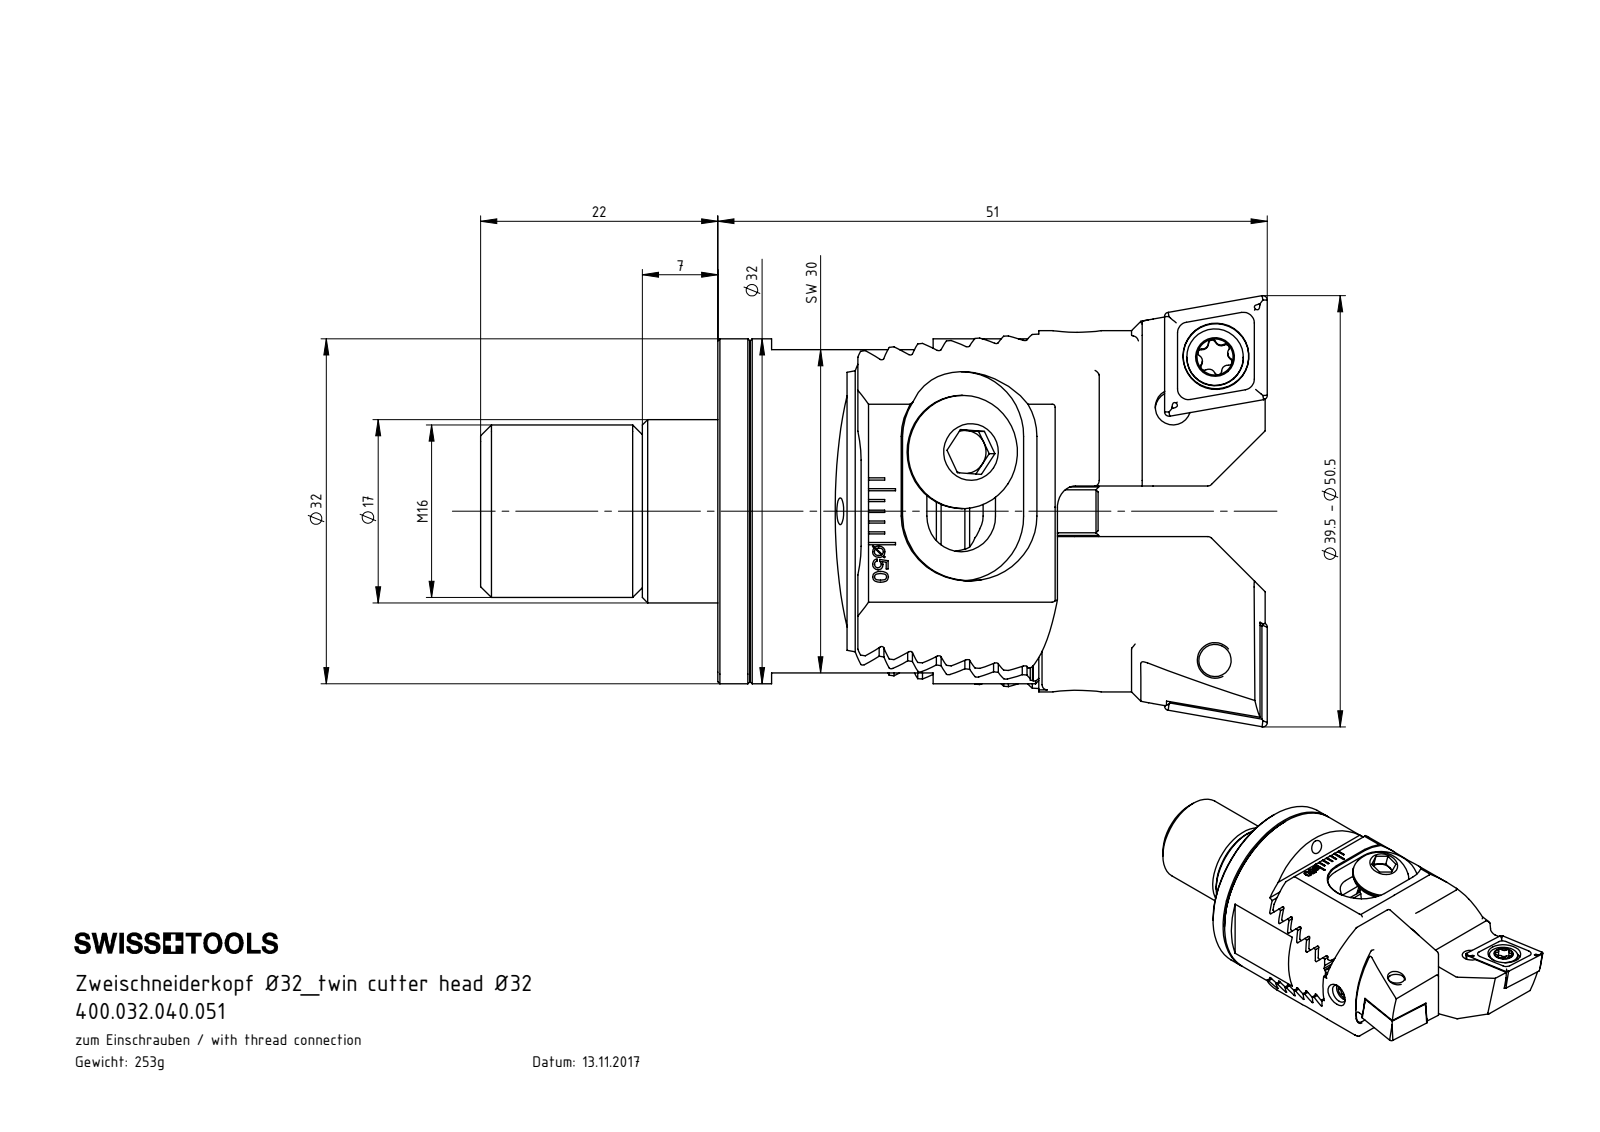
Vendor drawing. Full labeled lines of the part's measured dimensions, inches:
Part name (STEP PRODUCT): D32-D32.HP5.003_A; Z32-WCB.001.021; 400.032.040.051; HP5-ER2.012.030_A (+8 more)
STEP written by: SolidWorks 2017 (CONFIG_CONTROL_DESIGN)
Units: inches
Bodies: 16 solids, 985 faces (457 planar, 232 cylindrical, 296 other)
Overall size (bounding box): 2.874 × 1.575 × 1.26
Volume: 1.965 in³ · Surface area: 30.38 in²
Round holes (diameter × count): ⌀0.098 ×5, ⌀0.13 ×5, ⌀0.063 ×2, ⌀0.079 ×2, ⌀0.173 ×2, ⌀0.197 ×2, ⌀0.24 ×2, ⌀0.252 ×2, ⌀0.268 ×2, ⌀0.138 ×1, ⌀0.402 ×1, ⌀0.492 ×1
Round bosses / shafts (diameter × count): ⌀0.157 ×4, ⌀0.413 ×2, ⌀0.402 ×2, ⌀0.236 ×2, ⌀0.207 ×2, ⌀1.26 ×1, ⌀0.63 ×1, ⌀0.472 ×1
Partial cylindrical surfaces — rounded edges, fillets, slot ends (radius × count): R0.02 ×16, R0.008 ×14, R0.008 ×12, R0.013 ×12, R0.023 ×12, R0.079 ×4, R0.13 ×4, R0.236 ×4
Main face-to-face distances: 0.094, 0.187, 0.281, 0.118, 0.375, 0.375, 0.193, 0.469, 0.281, 0.096
Hole centre spacings: 0.239, 0.244, 0.954, 0.958, 1.128, 0.354, 0.355, 0.685
